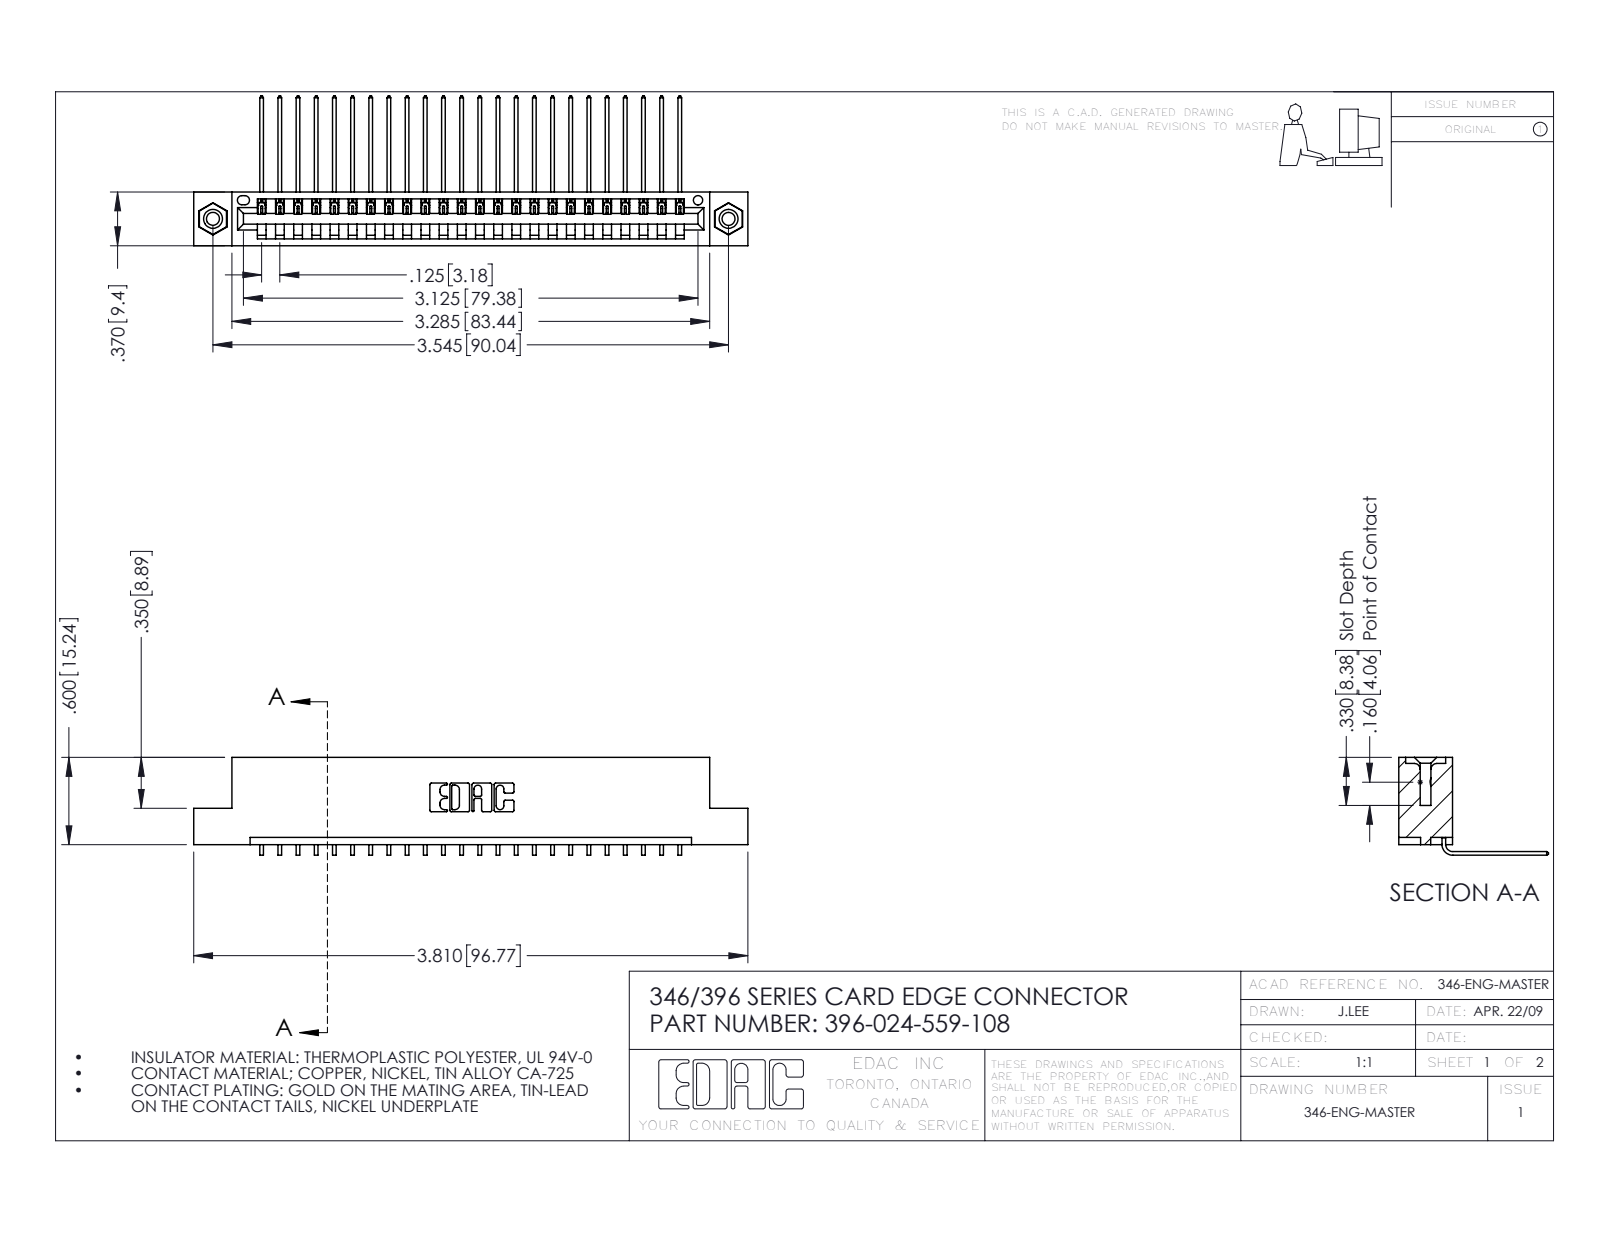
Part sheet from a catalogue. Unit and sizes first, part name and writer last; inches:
Units: inches
Overall size (bounding box): 3.81 × 1.03 × 0.673
Round holes (diameter × count): ⌀0.089 ×2, ⌀0.125 ×2, ⌀0.156 ×2, ⌀0.064 ×1
Round bosses / shafts (diameter × count): ⌀0.155 ×2
Partial cylindrical surfaces — rounded edges, fillets, slot ends (radius × count): R0.006 ×48, R0.01 ×22, R0.007 ×6, R0.031 ×6, R0.026 ×3, R0.031 ×2, R0.04 ×2, R0.014 ×1
Main face-to-face distances: 0.048, 0.322, 0.37, 0.25, 0.072, 0.025, 0.298, 0.148, 0.222, 0.1
Hole centre spacings: 0.246, 3.337, 3.545
Volume: 0.562 in³ · Surface area: 18.32 in²
Bodies: 27 solids, 1622 faces (1116 planar, 490 cylindrical, 16 other)
Part name (STEP PRODUCT): 346 Part_Flush Mounting Lugs - 0.156 Dia-TI; 345-292-001_558 559 Tail - 1; 345-250-001_345-250-003-102; 396-024-559-108
STEP written by: SolidWorks 2016 (CONFIG_CONTROL_DESIGN)
